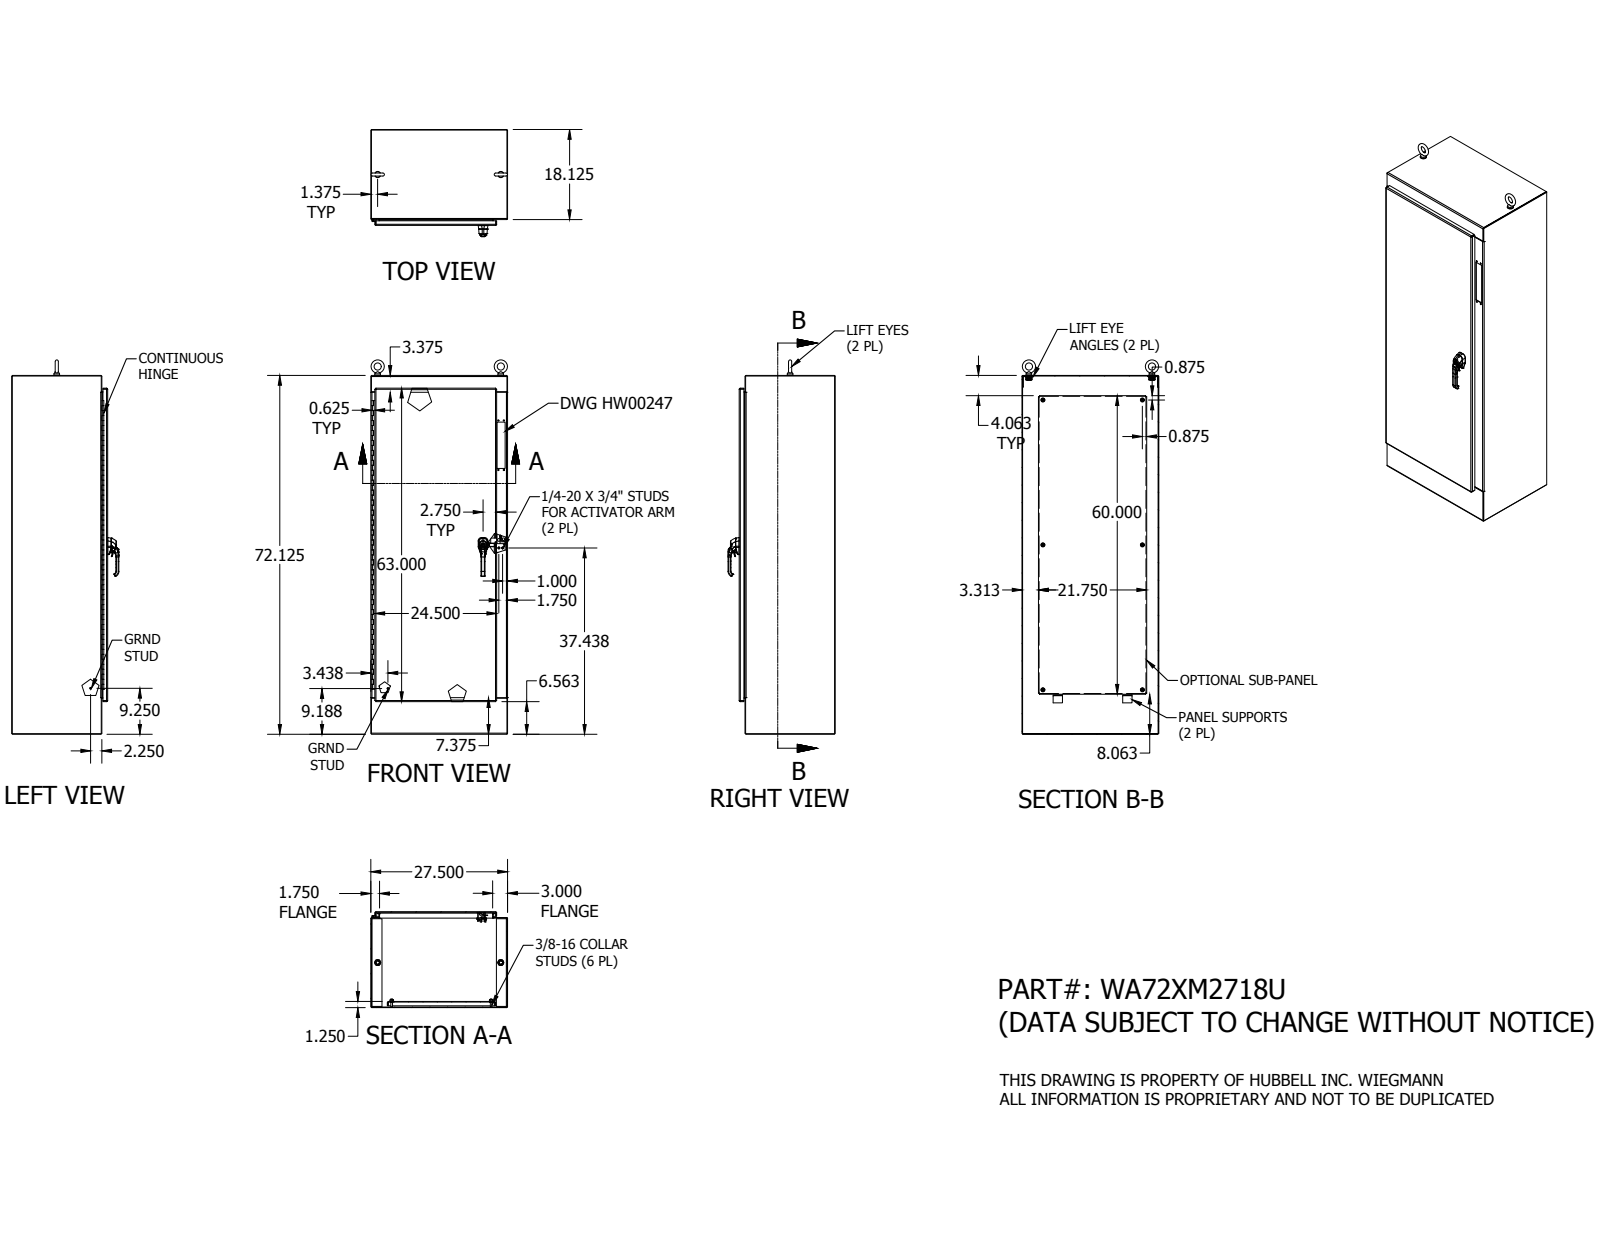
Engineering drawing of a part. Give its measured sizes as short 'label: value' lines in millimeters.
name: WA72XM27U_BACK; WA72XM18U_RIGHT_SIDE; WA72XM18U_LEFT_SIDE; WAXM2718U_TOP_ENDWALL (+8 more)
written by: Autodesk Inventor 2014 (AUTOMOTIVE_DESIGN)
unit: mm
bodies: 103 solids, 3698 faces (1615 planar, 1232 cylindrical, 851 other)
size: 1911.29 × 698.5 × 547.14
volume: 20 100 000 mm³; area: 12 920 000 mm²
holes: 10× ⌀9.52, 8× ⌀7.02, 7× ⌀7.14, 6× ⌀3.96, 6× ⌀6.35, 6× ⌀7.8, 6× ⌀14.29, 4× ⌀5.08, 4× ⌀7.37, 3× ⌀5.4, 2× ⌀3, 2× ⌀3.17
bosses: 10× ⌀15.88, 9× ⌀8.38, 6× ⌀14.29, 4× ⌀8.56, 4× ⌀6.35, 3× ⌀9.52, 3× ⌀6, 2× ⌀31.75
rounds: 187× R0.5, 108× R0.3, 48× R0.51, 21× R0.47, 21× R2.38, 20× R5.56, 14× R1.27, 14× R2
face distances: 3.17, 3.18, 28.58, 486.84, 483.67, 490.02, 486.85, 692.15, 695.32, 695.33
hole spacings: 467.26, 508, 9.67, 9.69, 9.72, 19.36, 19.4, 22.5
